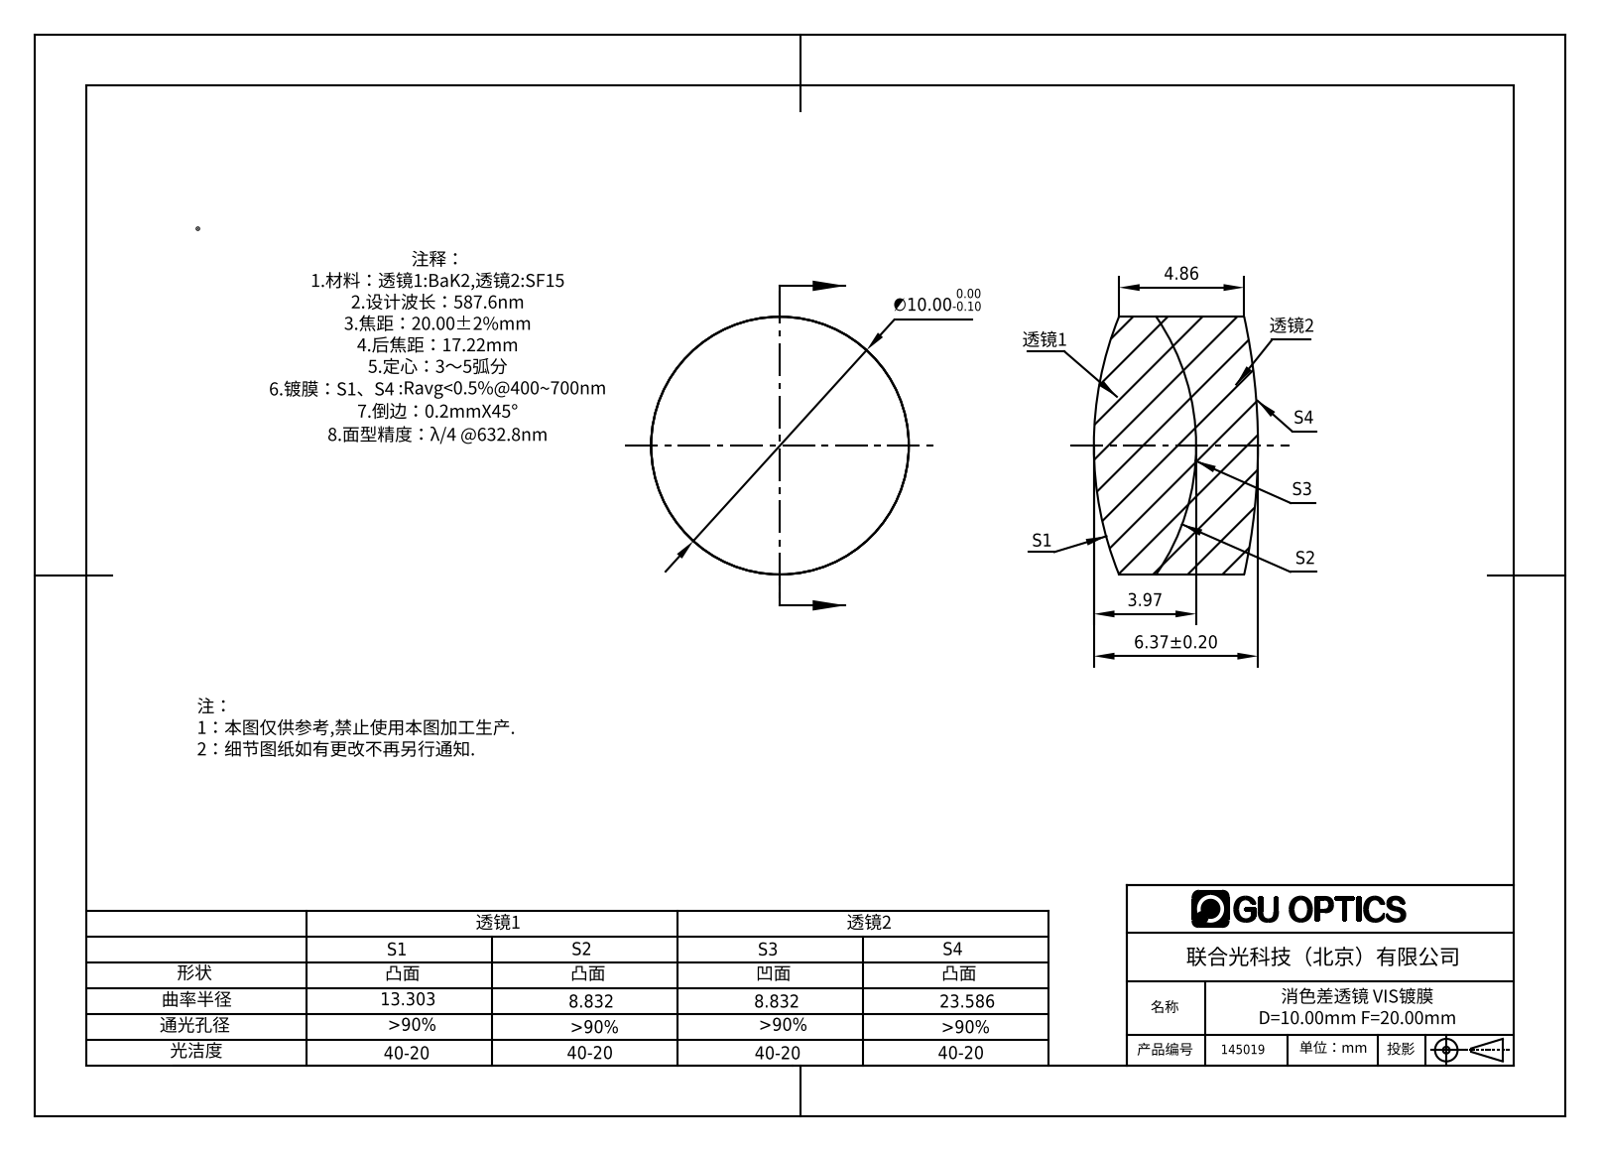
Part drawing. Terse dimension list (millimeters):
name: 145019
written by: SolidWorks 2016 (AUTOMOTIVE_DESIGN)
unit: mm
bodies: 2 solids, 12 faces (0 planar, 4 cylindrical, 8 other)
size: 10 × 10 × 6.37
volume: 442 mm³; area: 486 mm²
bosses: 1× ⌀10
